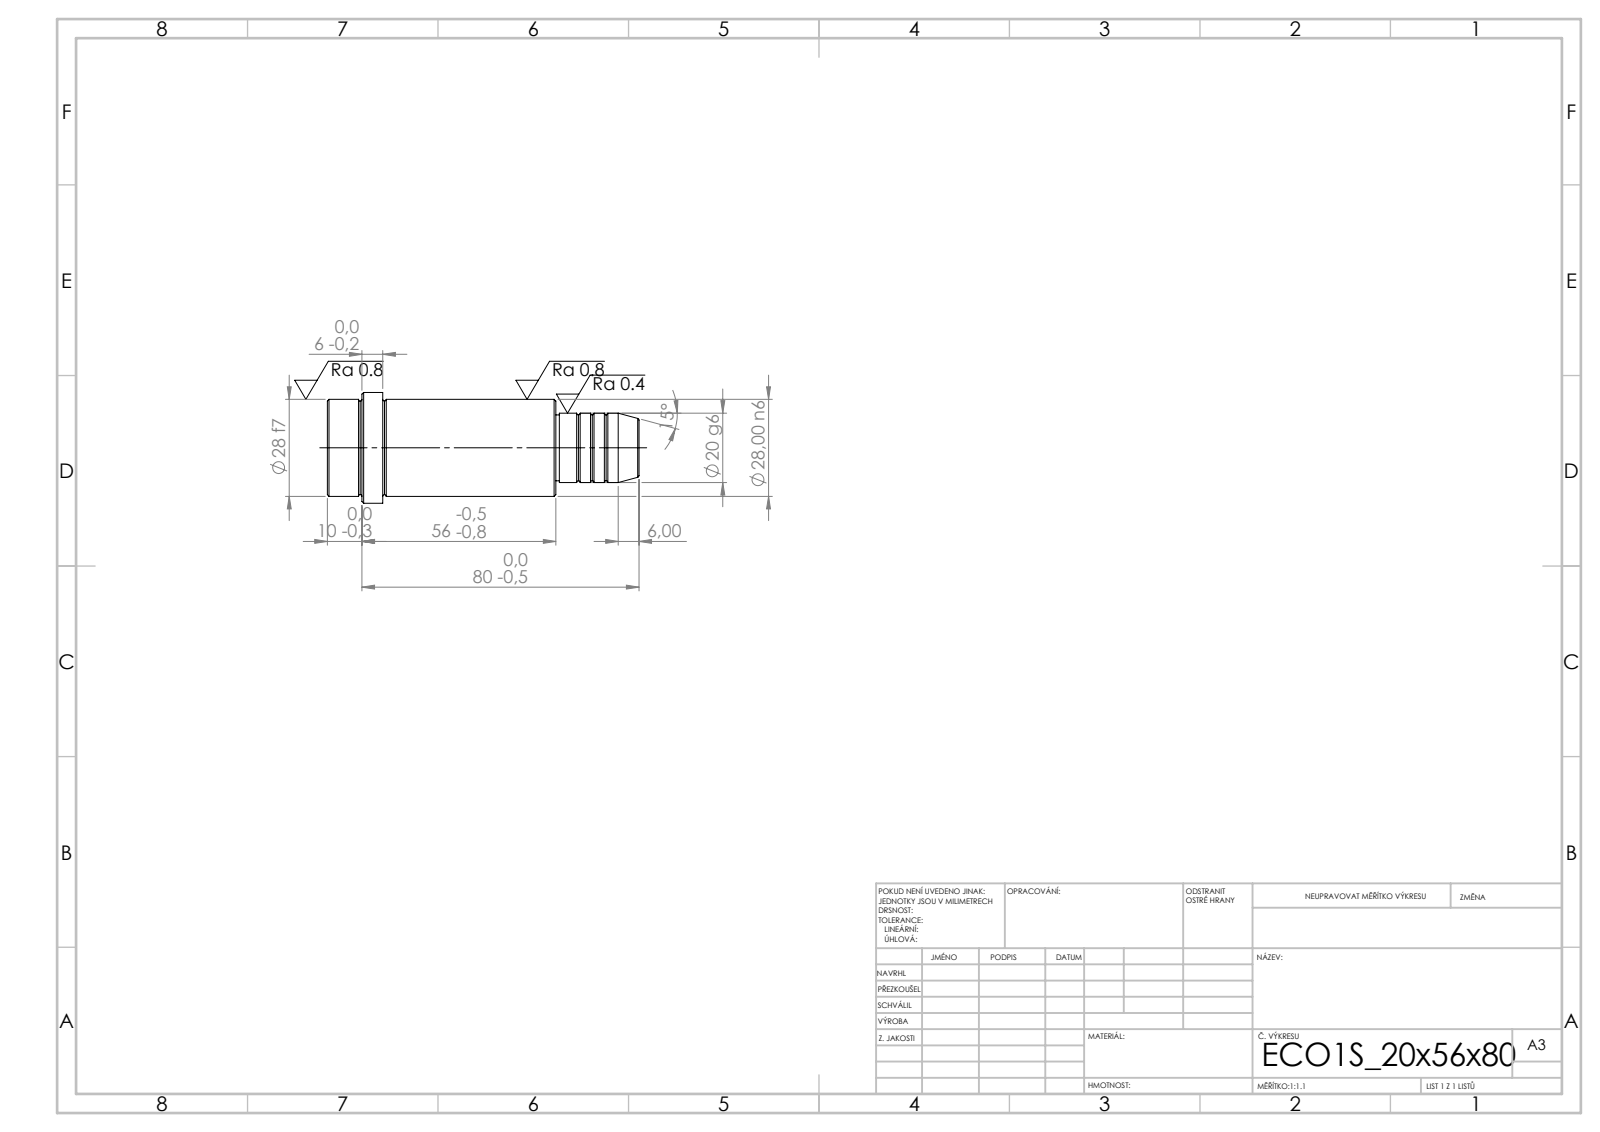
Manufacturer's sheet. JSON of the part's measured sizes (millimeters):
{"step_written_by": "SolidWorks 2019 (CONFIG_CONTROL_DESIGN)", "units": "millimeters", "bodies": {"solids": 1, "faces": 52, "planar": 6, "cylindrical": 16, "other": 30}, "overall_size": [90, 32, 32], "volume_mm3": 48817, "surface_area_mm2": 9049, "round_bosses_or_shafts": [[32, 1], [28, 1], [20, 1], [19, 1]], "face_to_face_distances": [66, 24, 90, 74, 50, 16, 80, 56, 6, 10]}
